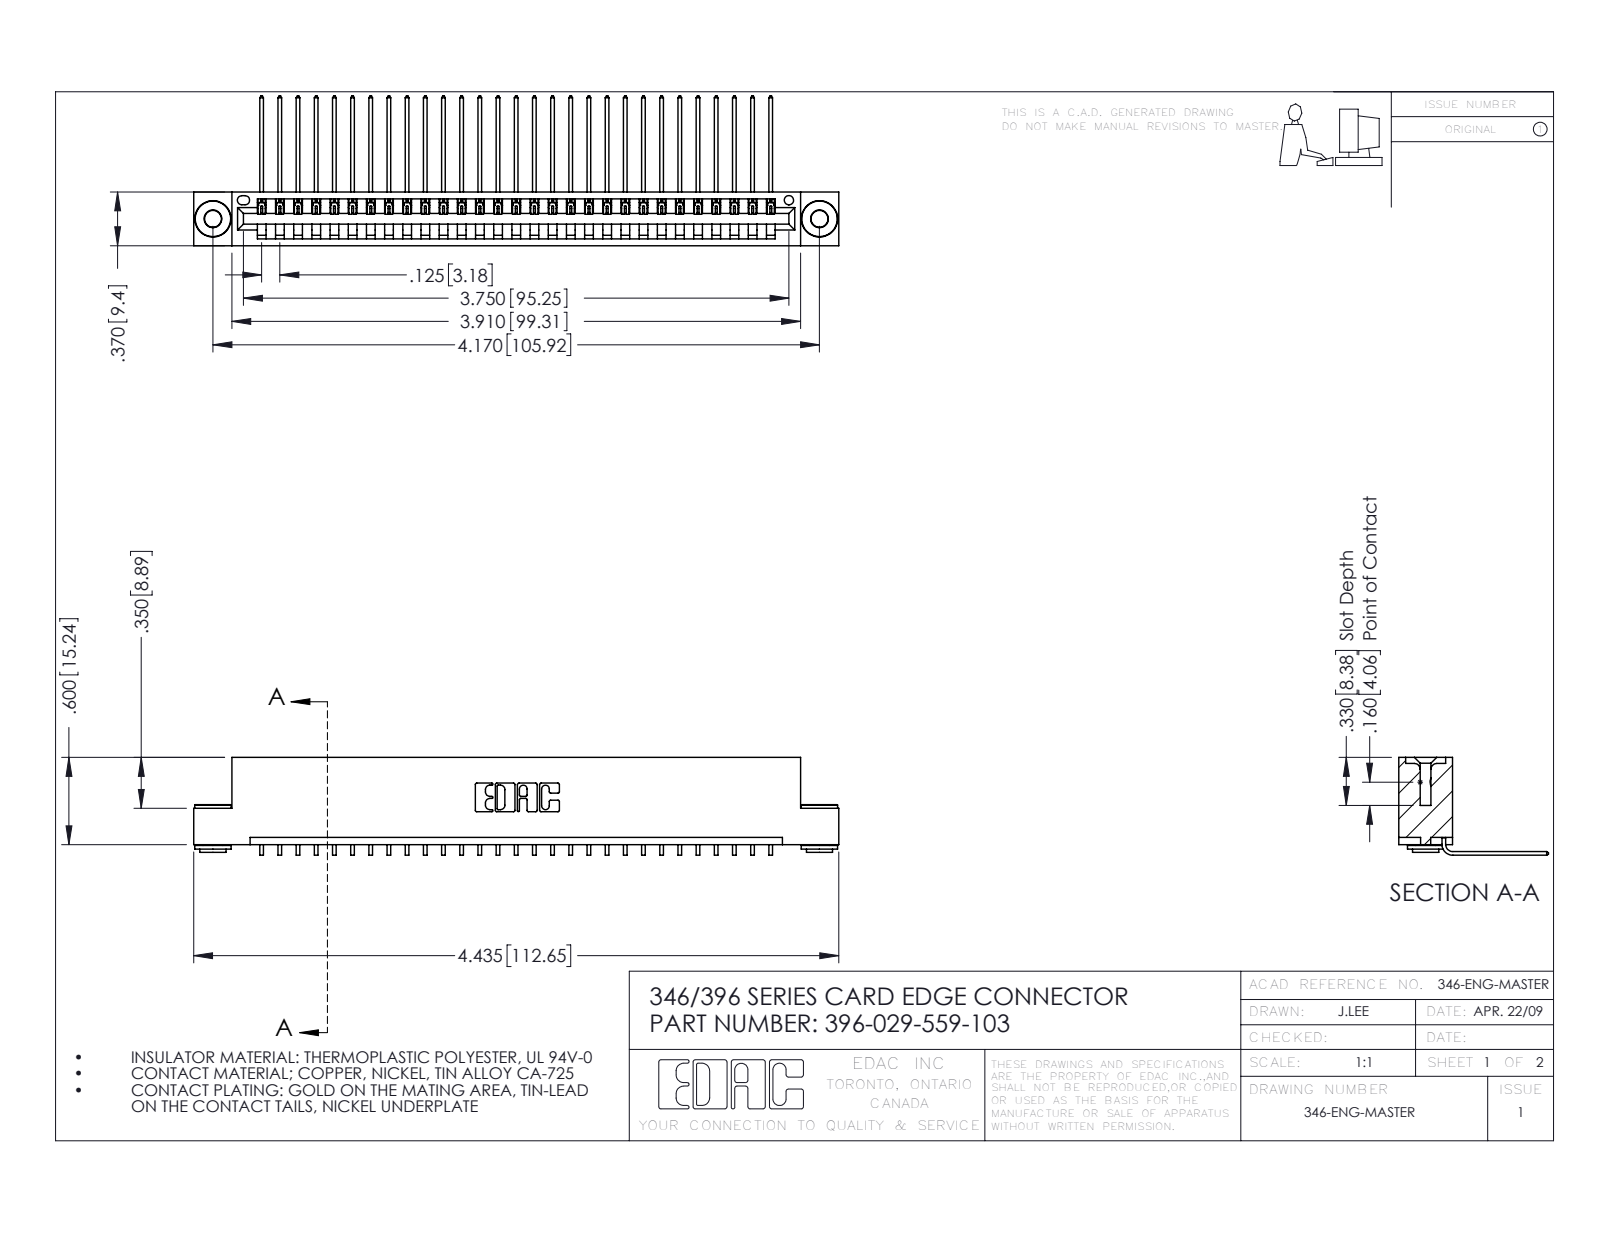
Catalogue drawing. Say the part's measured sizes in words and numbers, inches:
The part is named "346 Part_Flush Mounting Lugs - 0.156 Dia-TH; 345-292-001_558 559 Tail - 1; 345-250-002_345-250-002-102; 396-029-559-103". Its 3-D file was written by "SolidWorks 2016 (CONFIG_CONTROL_DESIGN)". It is 32 solids with 1900 faces: 1304 planar, 588 cylindrical and 8 other. Overall it measures 4.435 by 1.03 by 0.673 inches. Its volume is 0.66 cubic inches and its surface area 21.96 square inches. Round holes: 2 of diameter 0.116, 2 of diameter 0.156, 1 of diameter 0.064. Round bosses or shafts: 2 of diameter 0.25, 2 of diameter 0.18, 2 of diameter 0.136. Partial cylindrical surfaces (rounded edges, fillets, slot ends): 58 of radius 0.006, 22 of radius 0.01, 6 of radius 0.007, 6 of radius 0.031, 3 of radius 0.026, 2 of radius 0.031, 2 of radius 0.04, 1 of radius 0.014. The main face-to-face distances are 0.048, 0.322, 0.37, 0.25, 0.025, 0.072, 0.298, 0.148, 0.222, 0.1. The hole center spacings are 0.246, 3.962, 4.17.
